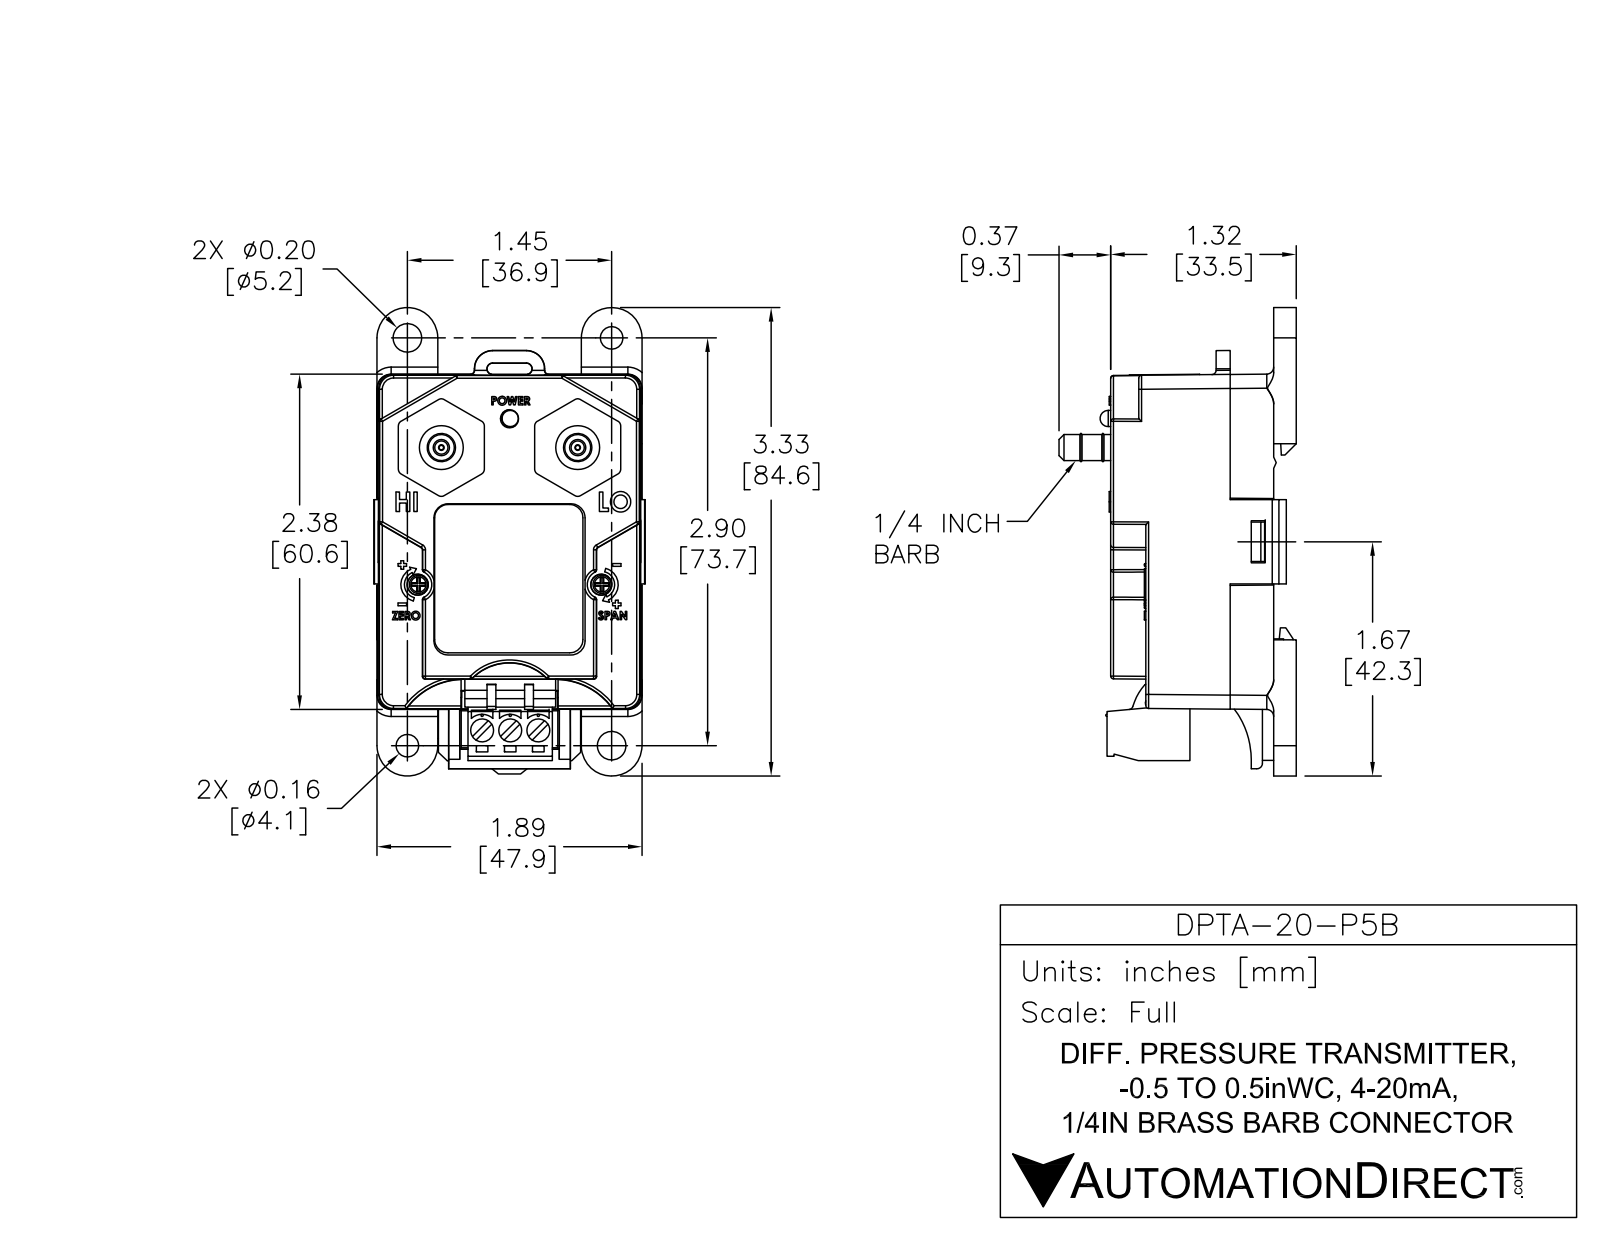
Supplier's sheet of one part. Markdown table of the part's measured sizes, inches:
| quantity | value |
| --- | --- |
| part name | DPTA-20-P5B |
| STEP written by | SolidWorks 2013 (AUTOMOTIVE_DESIGN) |
| units | inches |
| bodies | 11 solids, 506 faces (354 planar, 134 cylindrical, 18 other) |
| overall size | 3.347 × 1.959 × 1.697 |
| volume | 1.811 in³ |
| surface area | 53.85 in² |
| round holes (diameter × count) | 0.157 × 7, 0.098 × 2, 0.202 × 2, 0.122 × 1 |
| round bosses / shafts (diameter × count) | 0.197 × 3, 0.138 × 3, 0.138 × 3, 0.315 × 2, 0.187 × 2, 0.118 × 1 |
| partial cylindrical surfaces (radius × count) | 0.118 × 12, 0.079 × 4, 0.217 × 4, 0.039 × 2, 0.042 × 2, 0.044 × 2, 0.094 × 2, 0.128 × 2 |
| main face-to-face distances | 0.039, 0.075, 0.157, 1.146, 0.02, 1.846, 0.232, 0.197, 1.303, 1.071 |
| hole center spacings | 0.533, 0.816, 0.92, 0.981, 1.159, 1.357, 1.444, 1.505 |
